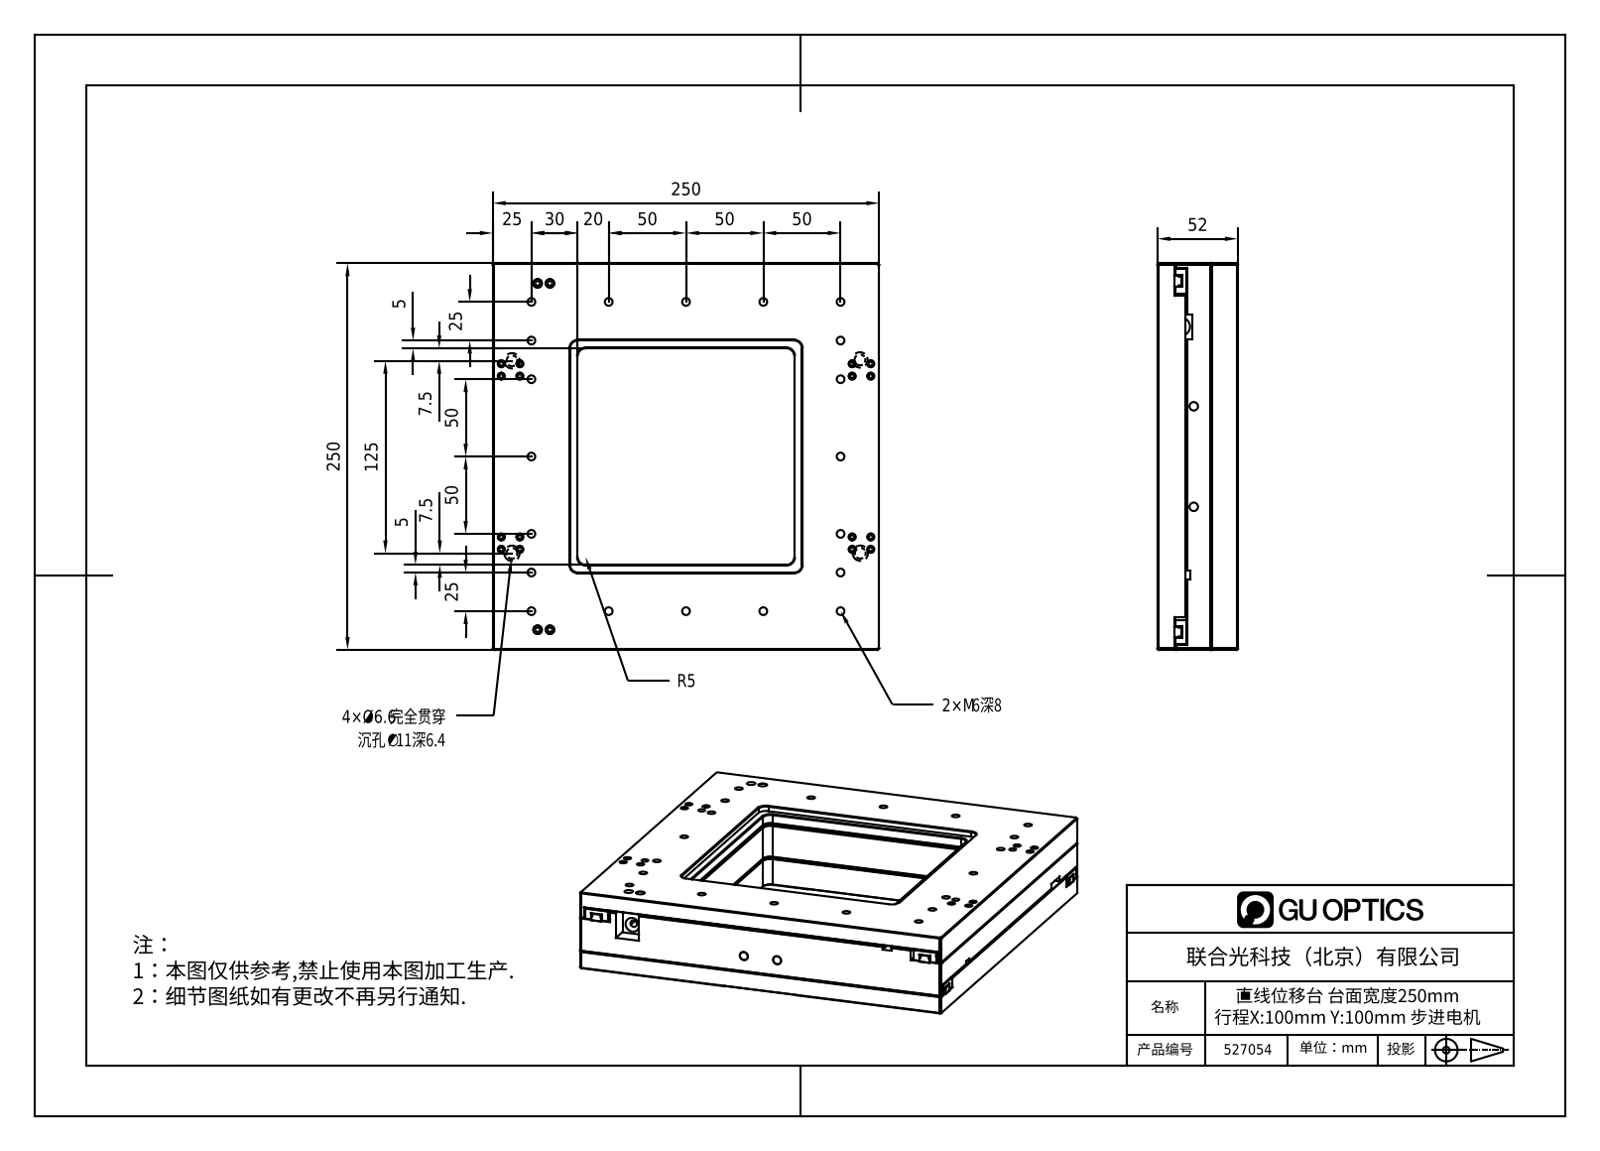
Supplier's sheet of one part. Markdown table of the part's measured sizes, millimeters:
| quantity | value |
| --- | --- |
| part name | FMSXY250Z-100 |
| STEP written by | SolidWorks 2017 (CONFIG_CONTROL_DESIGN) |
| units | millimeters |
| bodies | 0 solids, 570 faces (348 planar, 158 cylindrical, 64 other) |
| overall size | 250 × 250 × 52 |
| round holes (diameter × count) | 4.4 × 24, 5 × 20, 5.5 × 8, 6.6 × 4, 4.7 × 2, 6 × 2, 12.08 × 1 |
| partial cylindrical surfaces (radius × count) | 0.75 × 8, 5 × 8, 100 × 4 |
| main face-to-face distances | 23, 1, 10, 52, 33, 18, 19, 34, 42, 24 |
| hole center spacings | 50, 206.16, 100, 200, 201.56, 223.61, 150, 250 |
